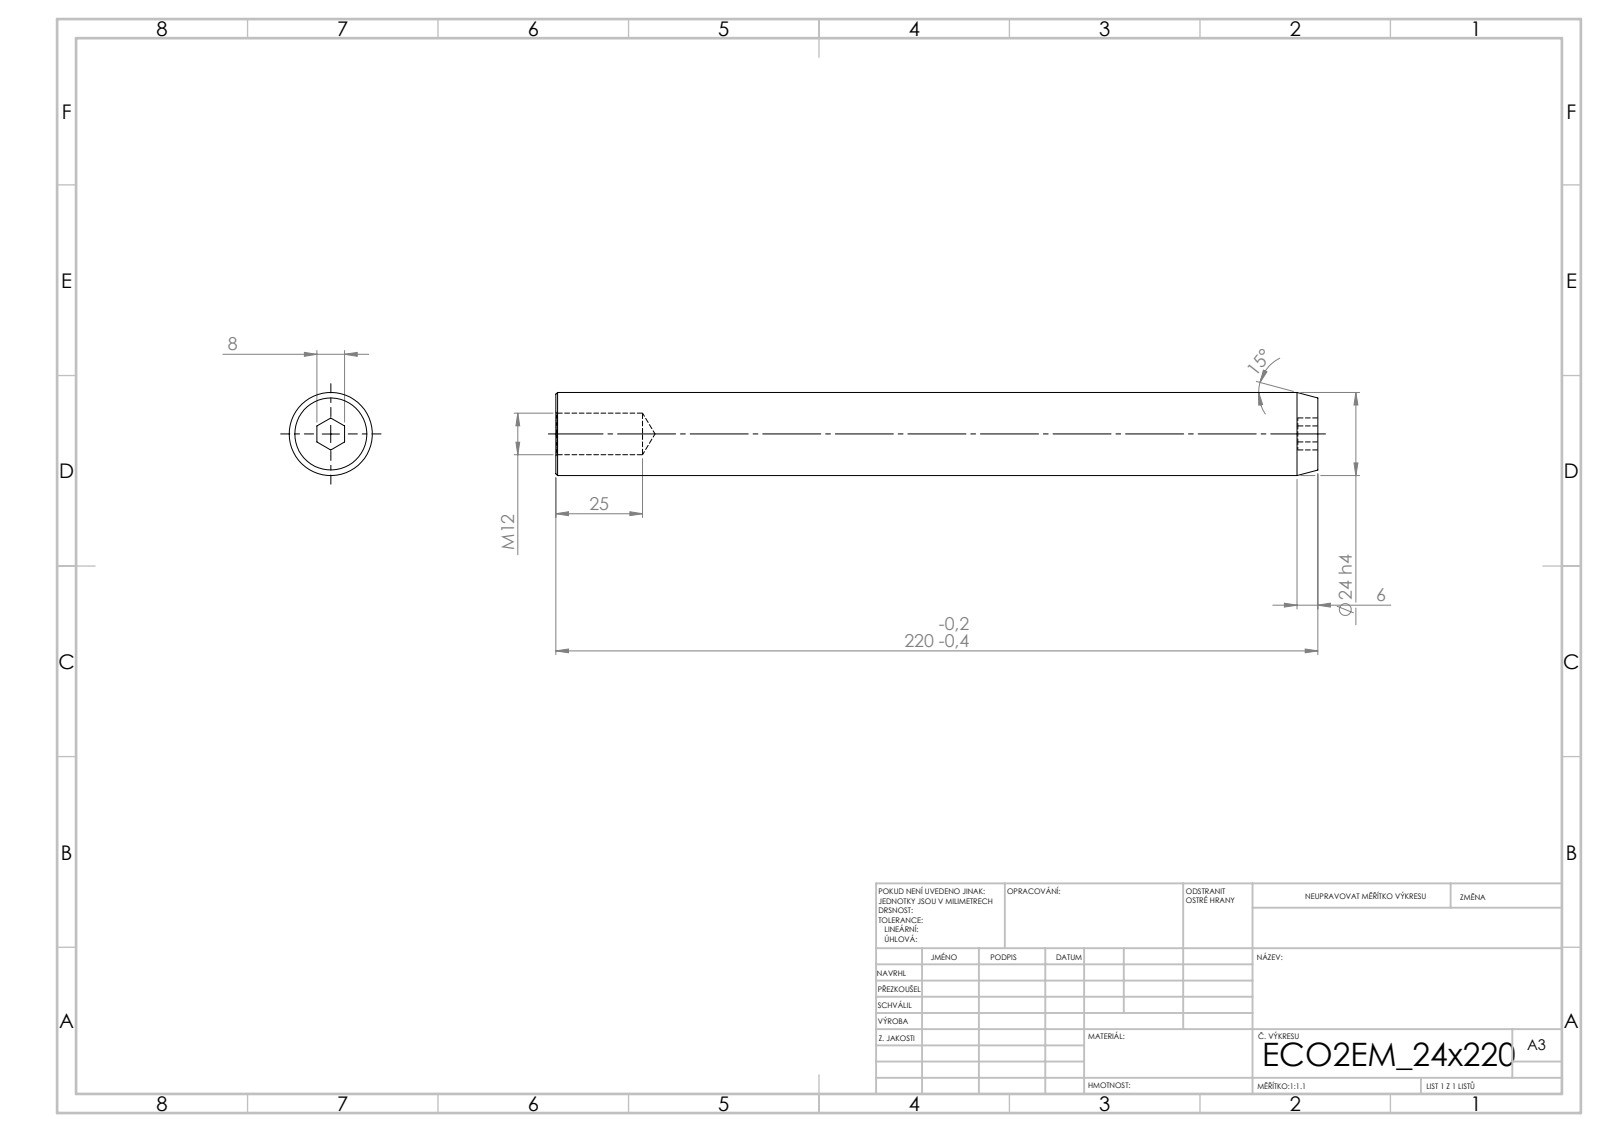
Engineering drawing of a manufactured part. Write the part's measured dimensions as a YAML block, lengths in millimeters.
step_written_by: "SolidWorks 2019 (CONFIG_CONTROL_DESIGN)"
units: millimeters
bodies: {solids: 1, faces: 21, planar: 9, cylindrical: 4, other: 8}
overall_size: [220, 24, 24]
volume: 95883
surface_area: 18459
round_holes:
  - {diameter: 12, count: 1}
round_bosses_or_shafts:
  - {diameter: 24, count: 1}
face_to_face_distances: [220, 8, 5.8, 214.2]
